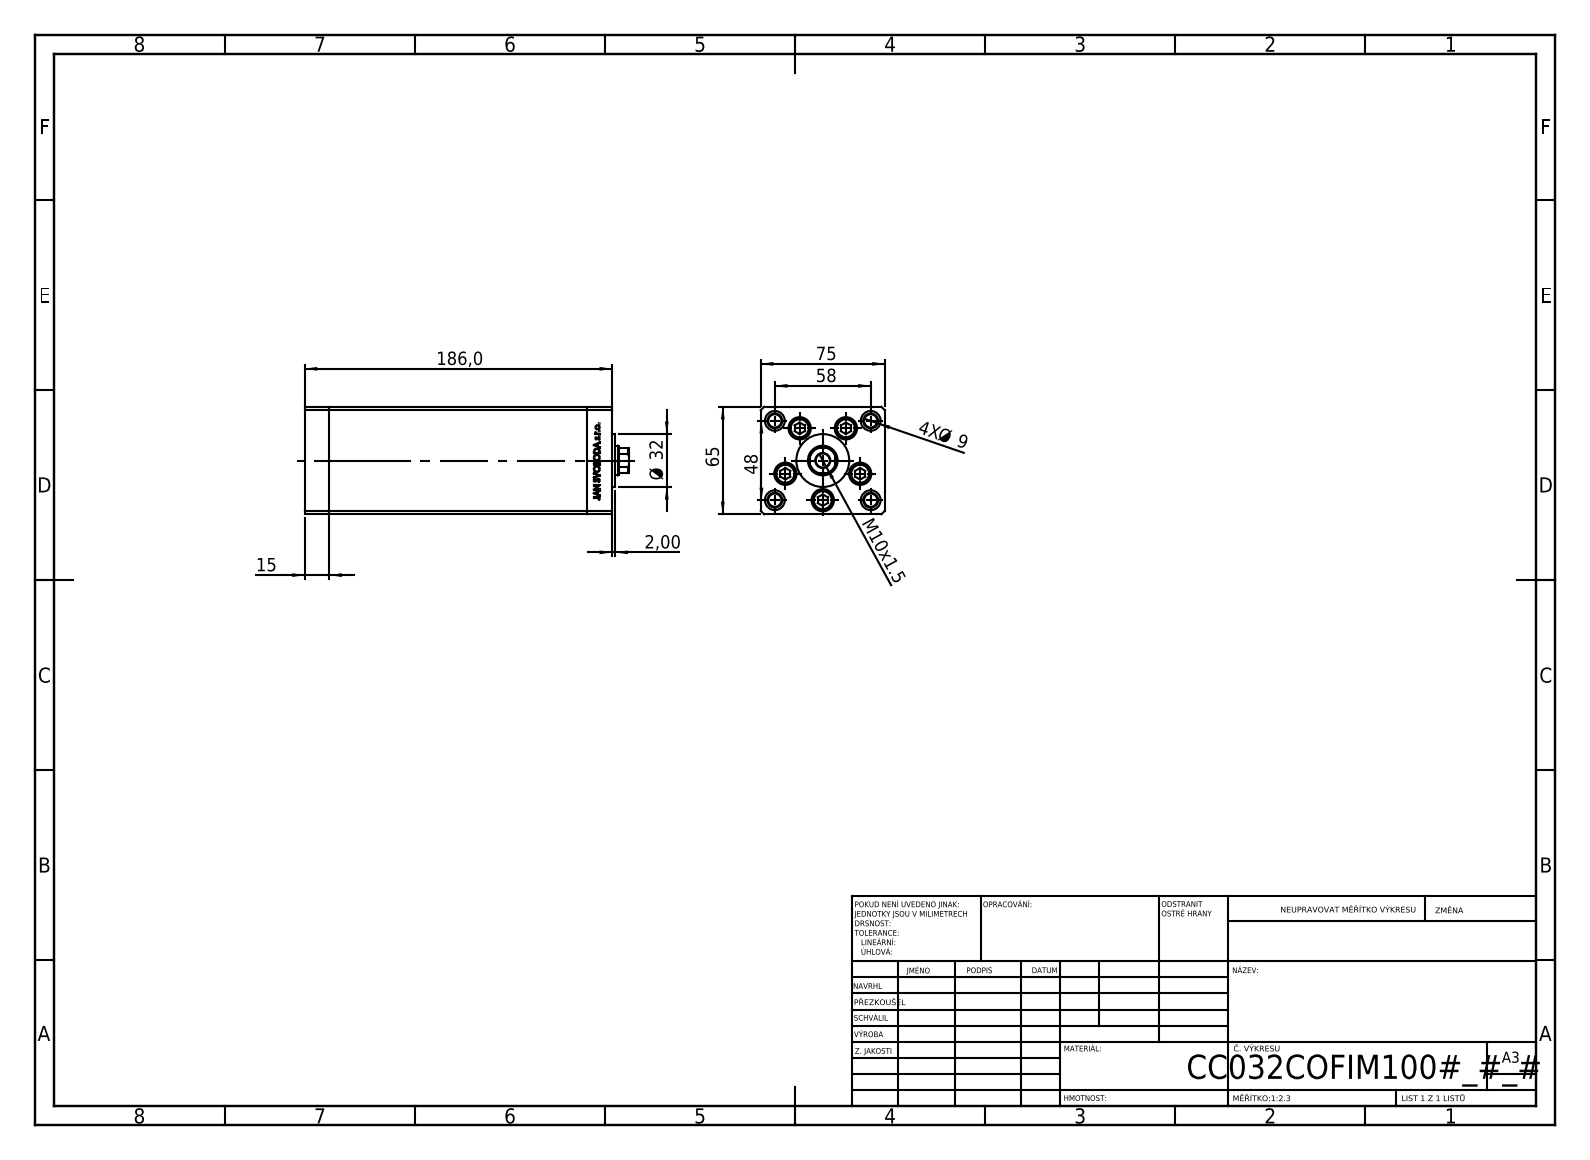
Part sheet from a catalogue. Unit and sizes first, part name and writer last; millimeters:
Units: millimetres
Overall size (bounding box): 196 × 75 × 65
Round holes (diameter × count): ⌀9 ×9, ⌀13.5 ×5, ⌀8 ×4, ⌀12 ×4, ⌀8.5 ×1, ⌀12.5 ×1, ⌀18 ×1
Round bosses / shafts (diameter × count): ⌀8 ×5, ⌀12.5 ×4, ⌀32 ×1
Partial cylindrical surfaces — rounded edges, fillets, slot ends (radius × count): R0.93 ×2, R8.5 ×1
Main face-to-face distances: 75, 65, 15, 156, 171, 186, 28, 54.5, 10.5, 26.25
Hole centre spacings: 24, 37.64, 15.67, 17.22, 27.71, 28.83, 29, 32.63
Volume: 761 493 mm³ · Surface area: 152 717 mm²
Bodies: 13 solids, 1159 faces (538 planar, 159 cylindrical, 462 other)
Part name (STEP PRODUCT): V220C FRONT; V220C_C MIDDLE; ALLEN BOLT; V220C BACK_C (+1 more)
STEP written by: SolidWorks 2019 (CONFIG_CONTROL_DESIGN)
